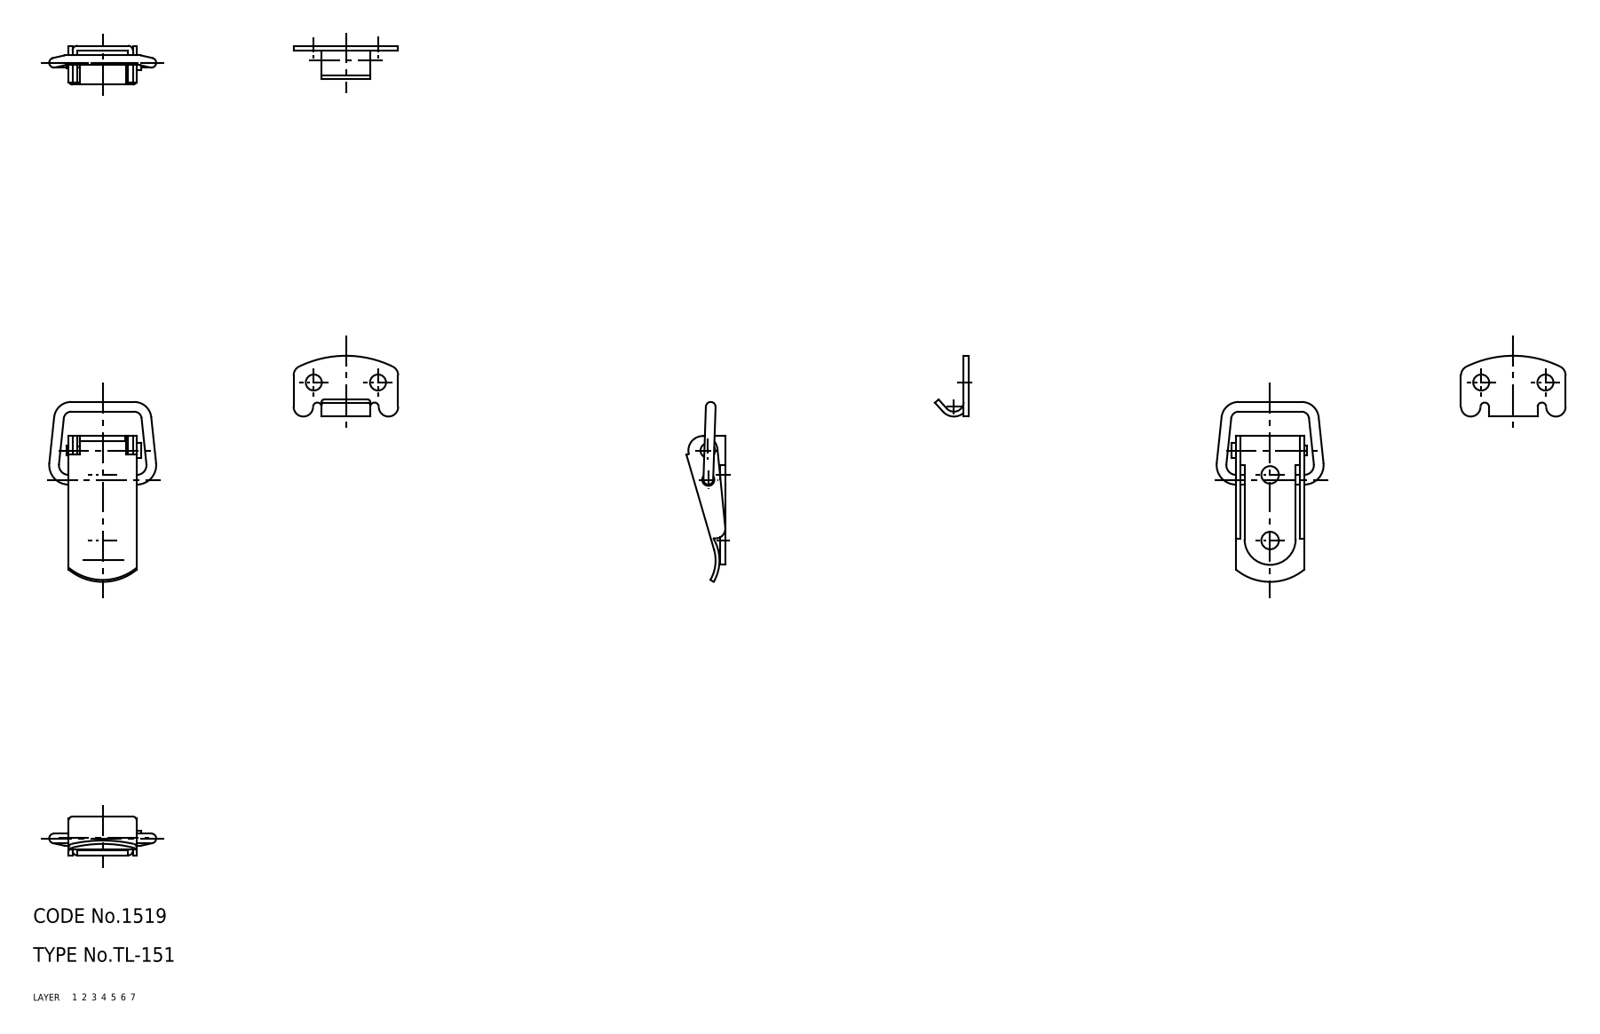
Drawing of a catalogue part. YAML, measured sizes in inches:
part_name: "67117721; 67117734; 67117747; 67117760 (+2 more)"
step_written_by: "CADfix (AUTOMOTIVE_DESIGN)"
units: inches
bodies: {solids: 6, faces: 159, planar: 0, cylindrical: 0, other: 159}
overall_size: [1.831, 0.87, 0.317]
volume: 0.079
surface_area: 5.23
